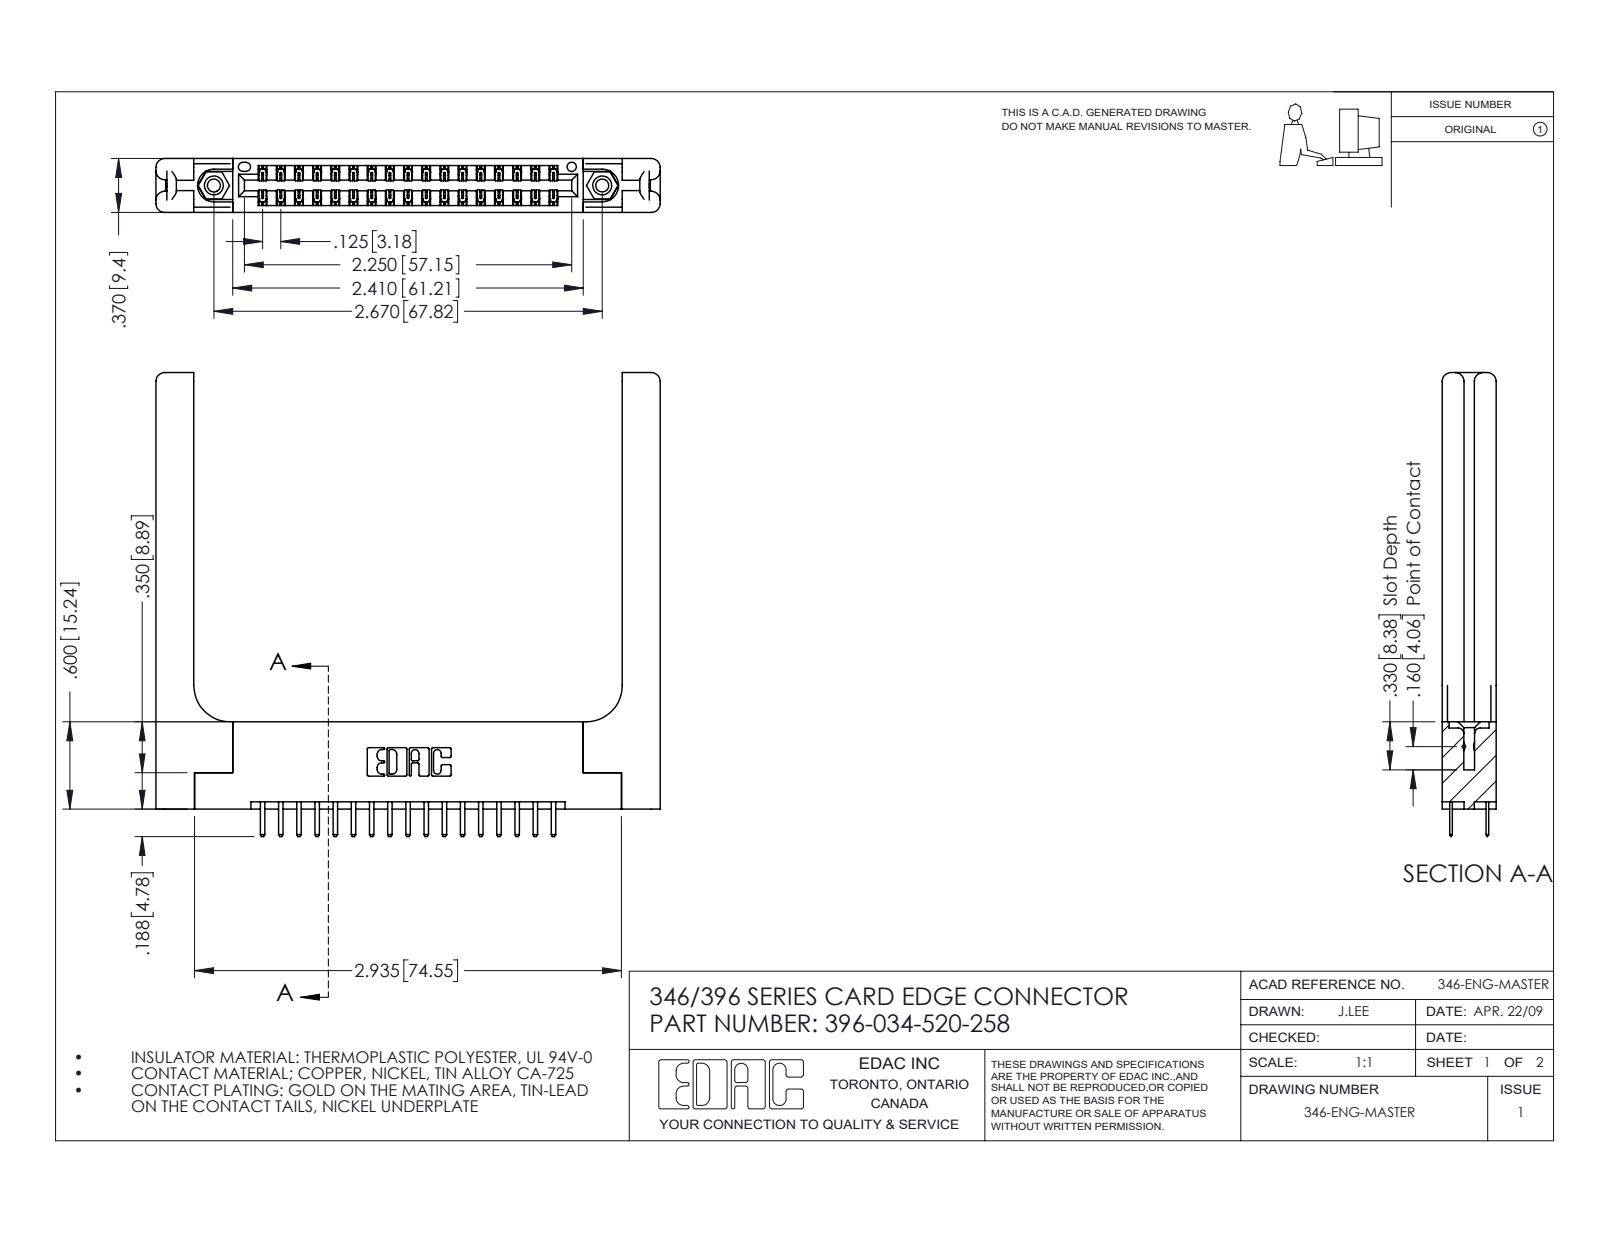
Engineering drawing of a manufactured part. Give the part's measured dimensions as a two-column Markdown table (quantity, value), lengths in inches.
| quantity | value |
| --- | --- |
| part name | 396-034-520-258; 346-220-058_345-220-058; 345-292-001_345-293-120; 346 Part_Flush Mounting Lugs - 0.156 Dia-TH (+1 more) |
| STEP written by | SolidWorks 2016 (CONFIG_CONTROL_DESIGN) |
| units | inches |
| bodies | 39 solids, 2282 faces (1482 planar, 740 cylindrical, 60 other) |
| overall size | 3.466 × 3.188 × 0.37 |
| volume | 0.968 in³ |
| surface area | 24.89 in² |
| round holes (diameter × count) | 0.089 × 2, 0.125 × 2, 0.156 × 2, 0.064 × 1 |
| round bosses / shafts (diameter × count) | 0.155 × 2 |
| partial cylindrical surfaces (radius × count) | 0.006 × 51, 0.01 × 38, 0.01 × 22, 0.06 × 16, 0.007 × 6, 0.031 × 6, 0.026 × 3, 0.014 × 2 |
| main face-to-face distances | 0.37, 0.15, 0.072, 0.148, 0.048, 0.322, 0.25, 0.102, 0.22, 0.173 |
| hole center spacings | 0.246, 2.463, 2.67 |
